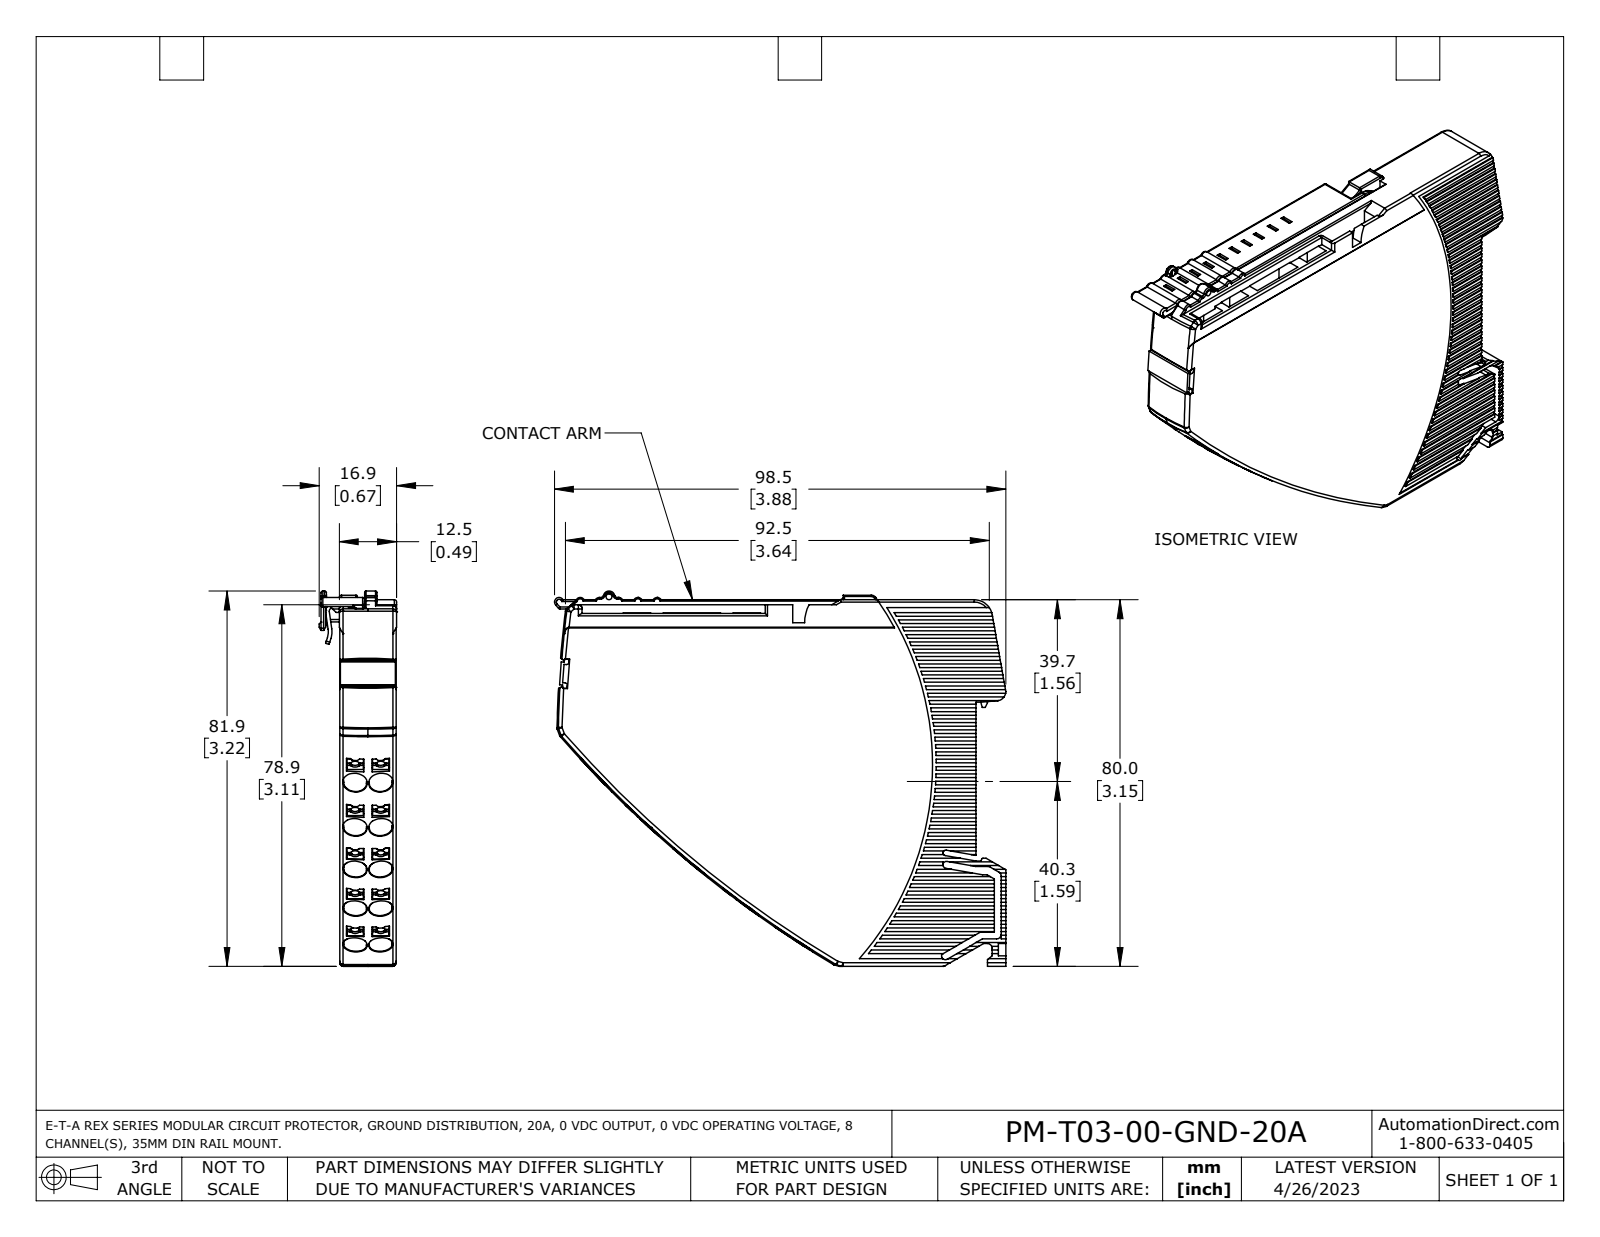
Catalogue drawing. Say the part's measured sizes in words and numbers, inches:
The part is named "t-pm12-t0x-00-gnd_ik00". Its 3-D file was written by "SolidWorks 2021 (AUTOMOTIVE_DESIGN)". It is 2 solids with 1707 faces: 1023 planar, 454 cylindrical and 230 other. Overall it measures 3.878 by 3.224 by 0.665 inches. Its volume is 4.249 cubic inches and its surface area 38.23 square inches. Round holes: 1 of diameter 0.051, 1 of diameter 0.161. Round bosses or shafts: 1 of diameter 0.157, 1 of diameter 0.079. Partial cylindrical surfaces (rounded edges, fillets, slot ends): 42 of radius 0.02, 40 of radius 0.012, 30 of radius 0.012, 27 of radius 0.016, 26 of radius 0.039, 20 of radius 0.098, 13 of radius 0.031, 10 of radius 0.008. The main face-to-face distances are 0.484, 0.476, 0.059, 0.205, 0.469, 0.264, 0.157, 0.061, 0.272, 0.146. The hole center spacings are 2.024.
